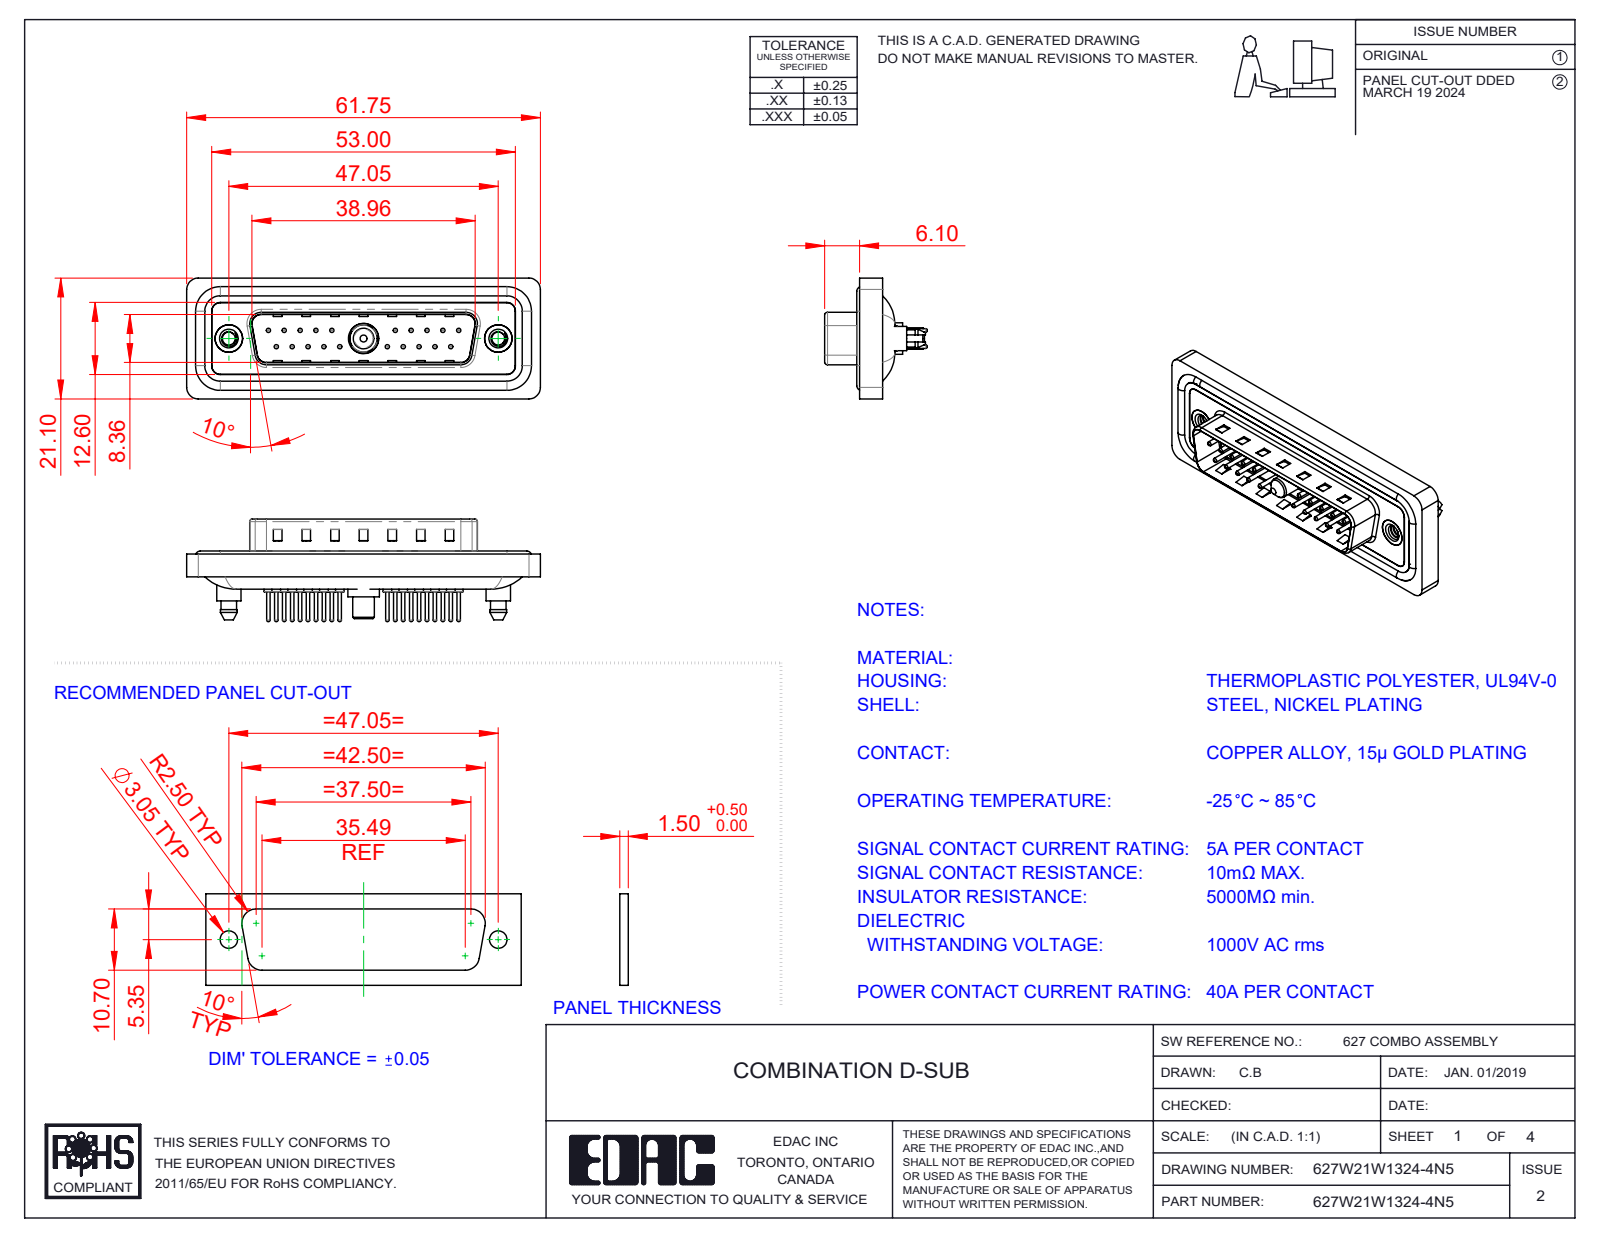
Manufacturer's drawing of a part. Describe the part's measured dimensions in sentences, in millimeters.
The part is named "Power Pin_40A S; 627Combo Shell Rear_25 Contacts; 627W21W1324-4N5; 627Combo Contact Row 2_24 (+5 more)". Its 3-D file was written by "SolidWorks 2023 (CONFIG_CONTROL_DESIGN)". It is 29 solids with 1312 faces: 375 planar, 519 cylindrical and 418 other. Overall it measures 61.75 by 21.1 by 17.9 millimeters. Its volume is 7 350 cubic millimeters and its surface area 12 297 square millimeters. Round holes: 20 of diameter 0.75, 20 of diameter 1.6, 20 of diameter 2, 2 of diameter 2.26, 2 of diameter 4, 2 of diameter 4.8, 2 of diameter 5, 1 of diameter 4.85, 1 of diameter 5.3. Round bosses or shafts: 20 of diameter 1.5, 20 of diameter 0.6, 4 of diameter 1.6, 2 of diameter 5.4, 2 of diameter 4.9, 2 of diameter 4.25, 1 of diameter 5.5, 1 of diameter 5.2. Partial cylindrical surfaces (rounded edges, fillets, slot ends): 24 of radius 1.5, 18 of radius 2, 10 of radius 1.6, 8 of radius 0.5, 4 of radius 0.25, 4 of radius 0.6, 4 of radius 0.65, 4 of radius 0.9. The main face-to-face distances are 0.4, 1.5, 1.1, 1.6, 3.1, 0.5, 2.9, 4.1, 0.82, 9.58. The hole center spacings are 3.16, 2.77, 5.54, 8.31, 5.04, 19.39, 20.97, 22.16.
